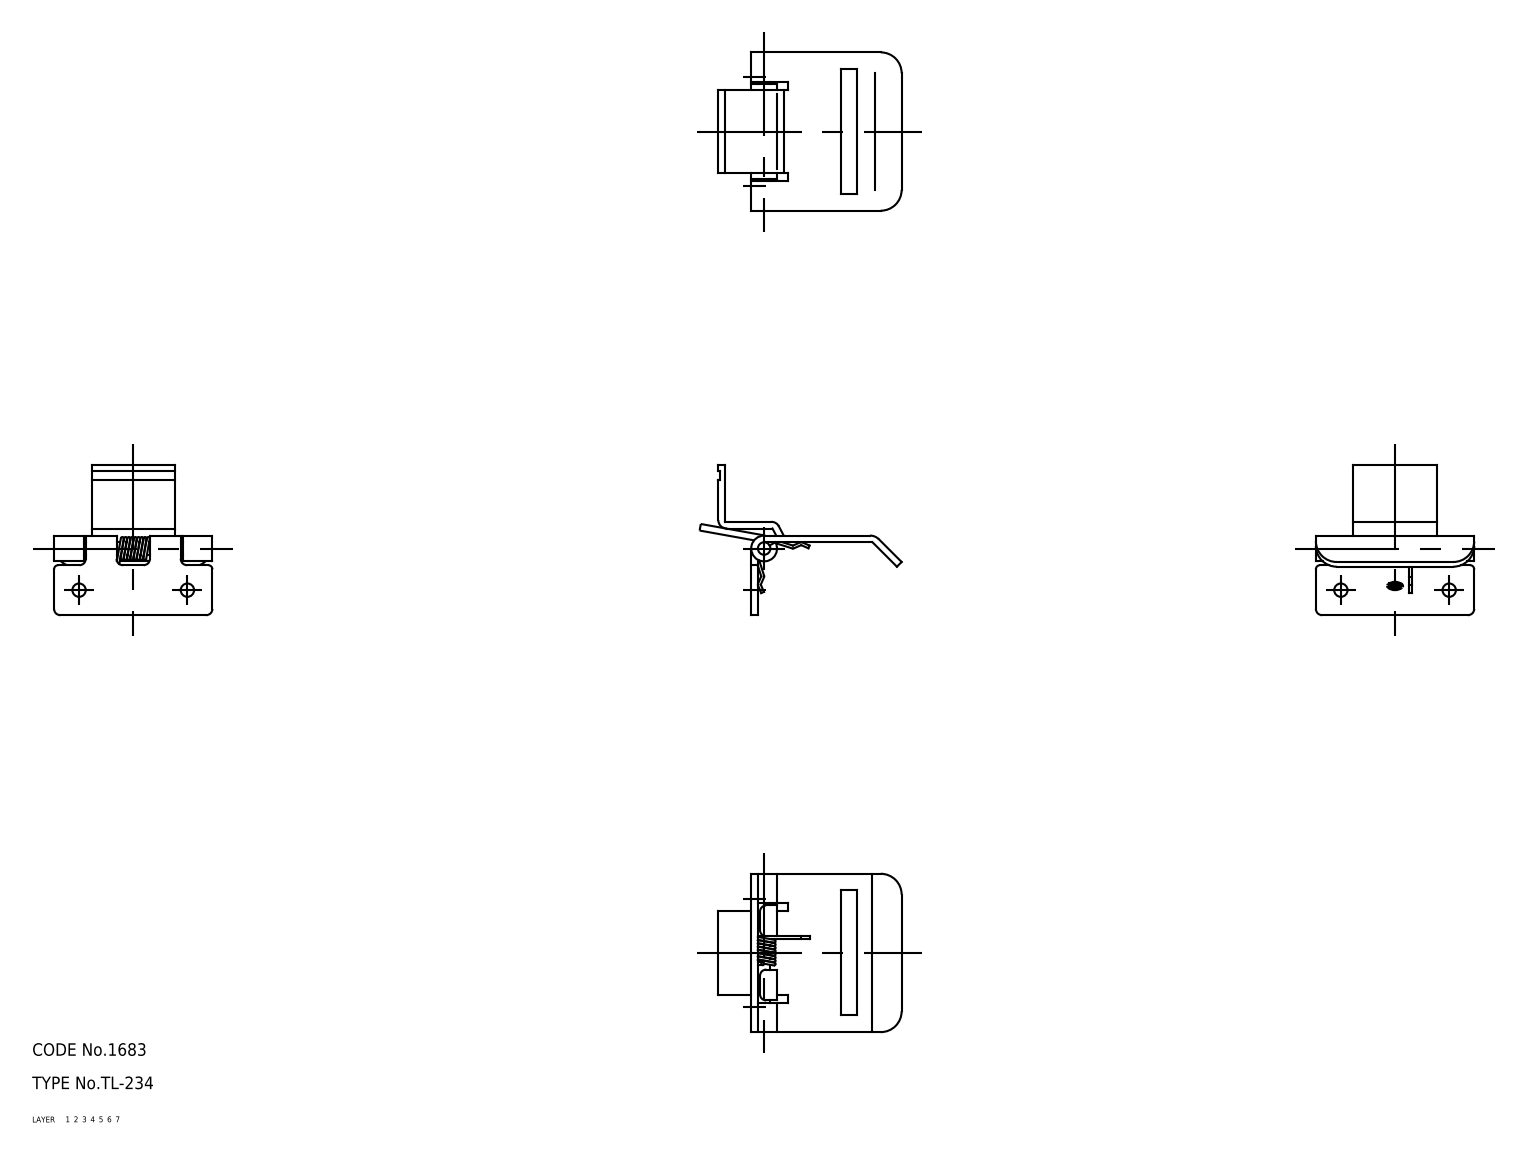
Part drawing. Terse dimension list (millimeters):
name: spring; shaft; base; latch (+1 more)
written by: CADfix (AUTOMOTIVE_DESIGN)
unit: mm
bodies: 4 solids, 96 faces (0 planar, 0 cylindrical, 96 other)
size: 44 × 38 × 36
volume: 4 365 mm³; area: 6 643 mm²
